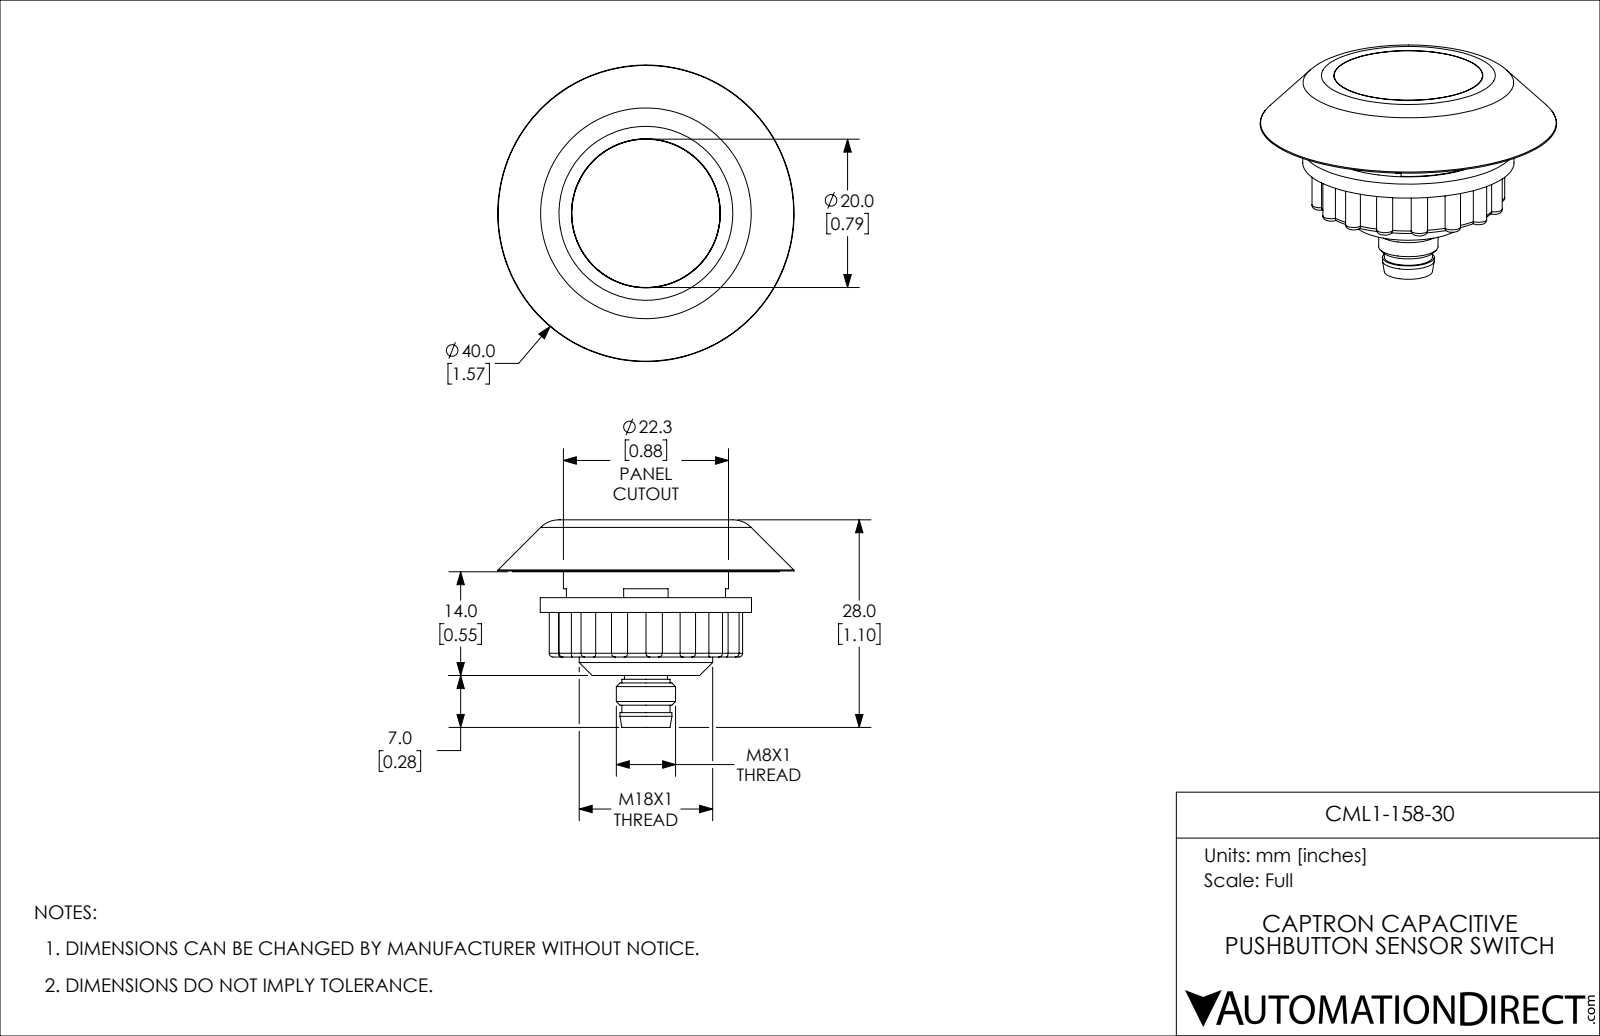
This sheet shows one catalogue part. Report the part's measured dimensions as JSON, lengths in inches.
{"part_name": "CML1-158-30", "step_written_by": "SolidWorks 2019 (CONFIG_CONTROL_DESIGN)", "units": "inches", "bodies": {"solids": 10, "faces": 218, "planar": 40, "cylindrical": 99, "other": 79}, "overall_size": [1.575, 1.575, 1.102], "volume_in3": 0.659, "surface_area_in2": 13.85, "round_holes": [[0.079, 2], [0.236, 1], [0.669, 1], [0.791, 1], [0.89, 1], [0.906, 1], [1.457, 1]], "round_bosses_or_shafts": [[0.039, 4], [1.417, 1], [1.122, 1], [0.877, 1], [0.709, 1], [0.315, 1], [0.276, 1], [0.256, 1]], "partial_cylinders_radius": [[0.043, 16], [0.39, 1], [0.472, 1]], "face_to_face_distances": [0.118, 0.039, 0.236, 0.157, 0.413, 0.295, 0.276, 0.177, 0.138, 0.492], "hole_center_spacings": [0.217, 0.433]}
